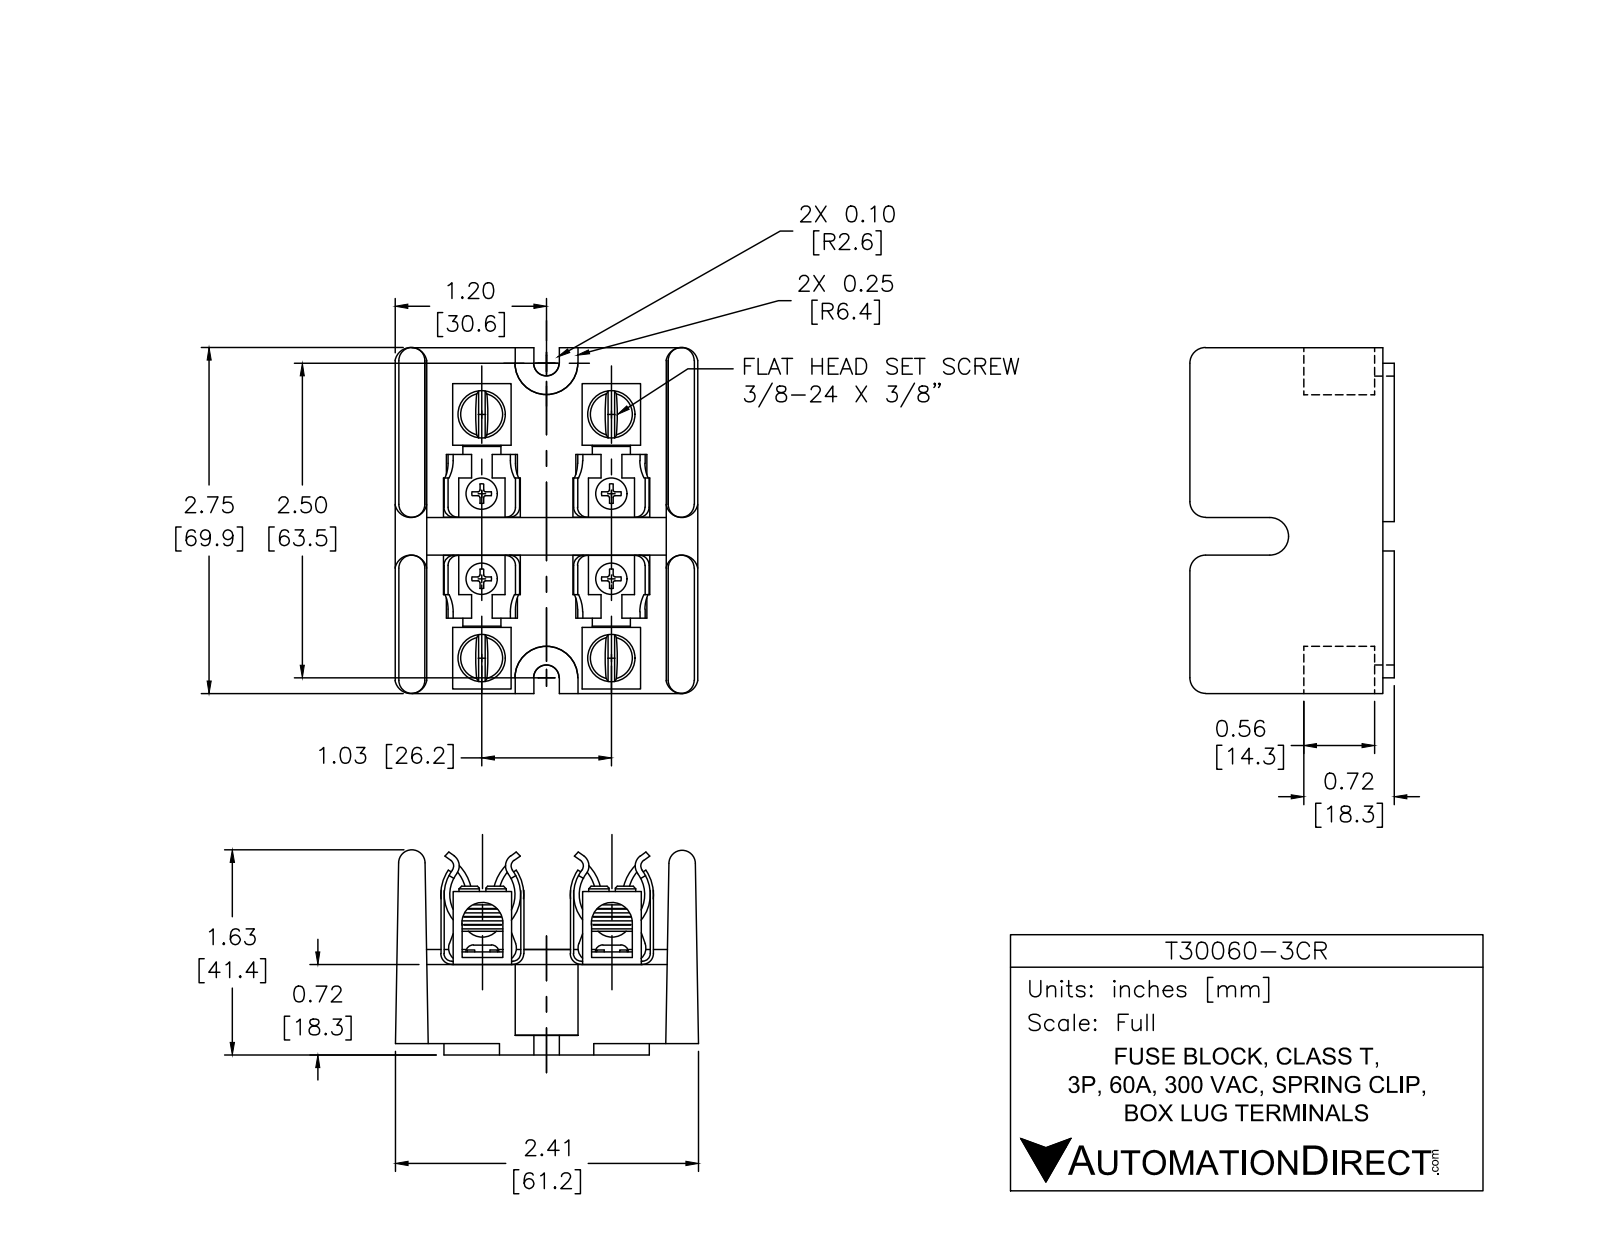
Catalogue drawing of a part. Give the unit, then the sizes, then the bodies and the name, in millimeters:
Units: millimetres
Overall size (bounding box): 69.9 × 61.2 × 41.4
Round holes (diameter × count): ⌀8.1 ×4
Round bosses / shafts (diameter × count): ⌀8 ×4
Partial cylindrical surfaces — rounded edges, fillets, slot ends (radius × count): R5.1 ×16, R3.2 ×15, R6.1 ×8, R6.4 ×4, R2.5 ×2, R4.1 ×2, R7.4 ×2, R9.5 ×2
Main face-to-face distances: 17.3, 6.4, 61.2, 54.8, 1.5, 18.8, 48.5, 1, 11.4, 49.8
Hole centre spacings: 26.2, 51.1, 57.4
Volume: 100 400 mm³ · Surface area: 33 440 mm²
Bodies: 9 solids, 319 faces (148 planar, 139 cylindrical, 32 other)
Part name (STEP PRODUCT): T30060-2CR
STEP written by: SolidWorks 2019 (AUTOMOTIVE_DESIGN)
